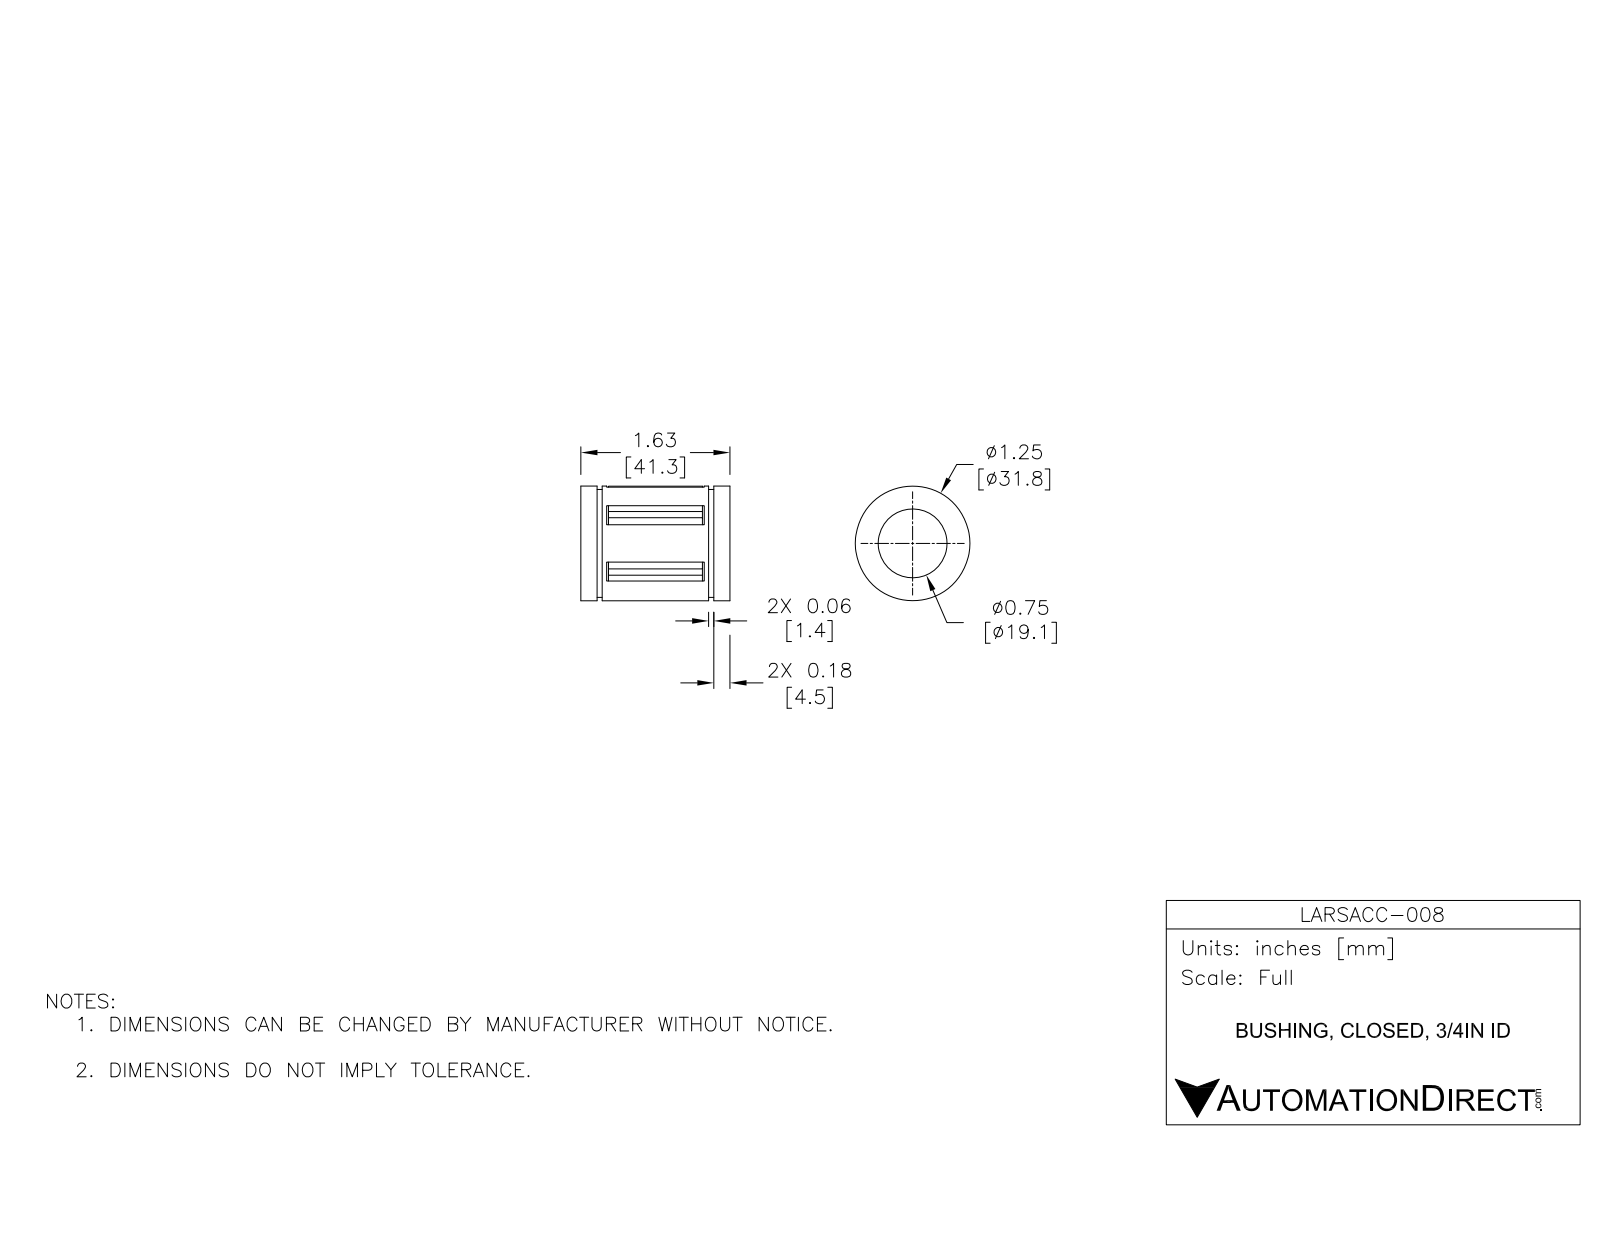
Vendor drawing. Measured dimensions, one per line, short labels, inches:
name: LARSACC-008
written by: SolidWorks 2015 (AUTOMOTIVE_DESIGN)
unit: in
bodies: 1 solid, 65 faces (36 planar, 29 cylindrical, 0 other)
size: 1.625 × 1.25 × 1.25
volume: 1.258 in³; area: 12.39 in²
holes: 1× ⌀0.75
bosses: 1× ⌀1.25, 1× ⌀1.176
rounds: 6× R0.517, 5× R0.615
face distances: 1.625, 1.216, 0.056, 0.176, 1.393, 1.449, 0.233, 0.232, 1.448, 1.272
